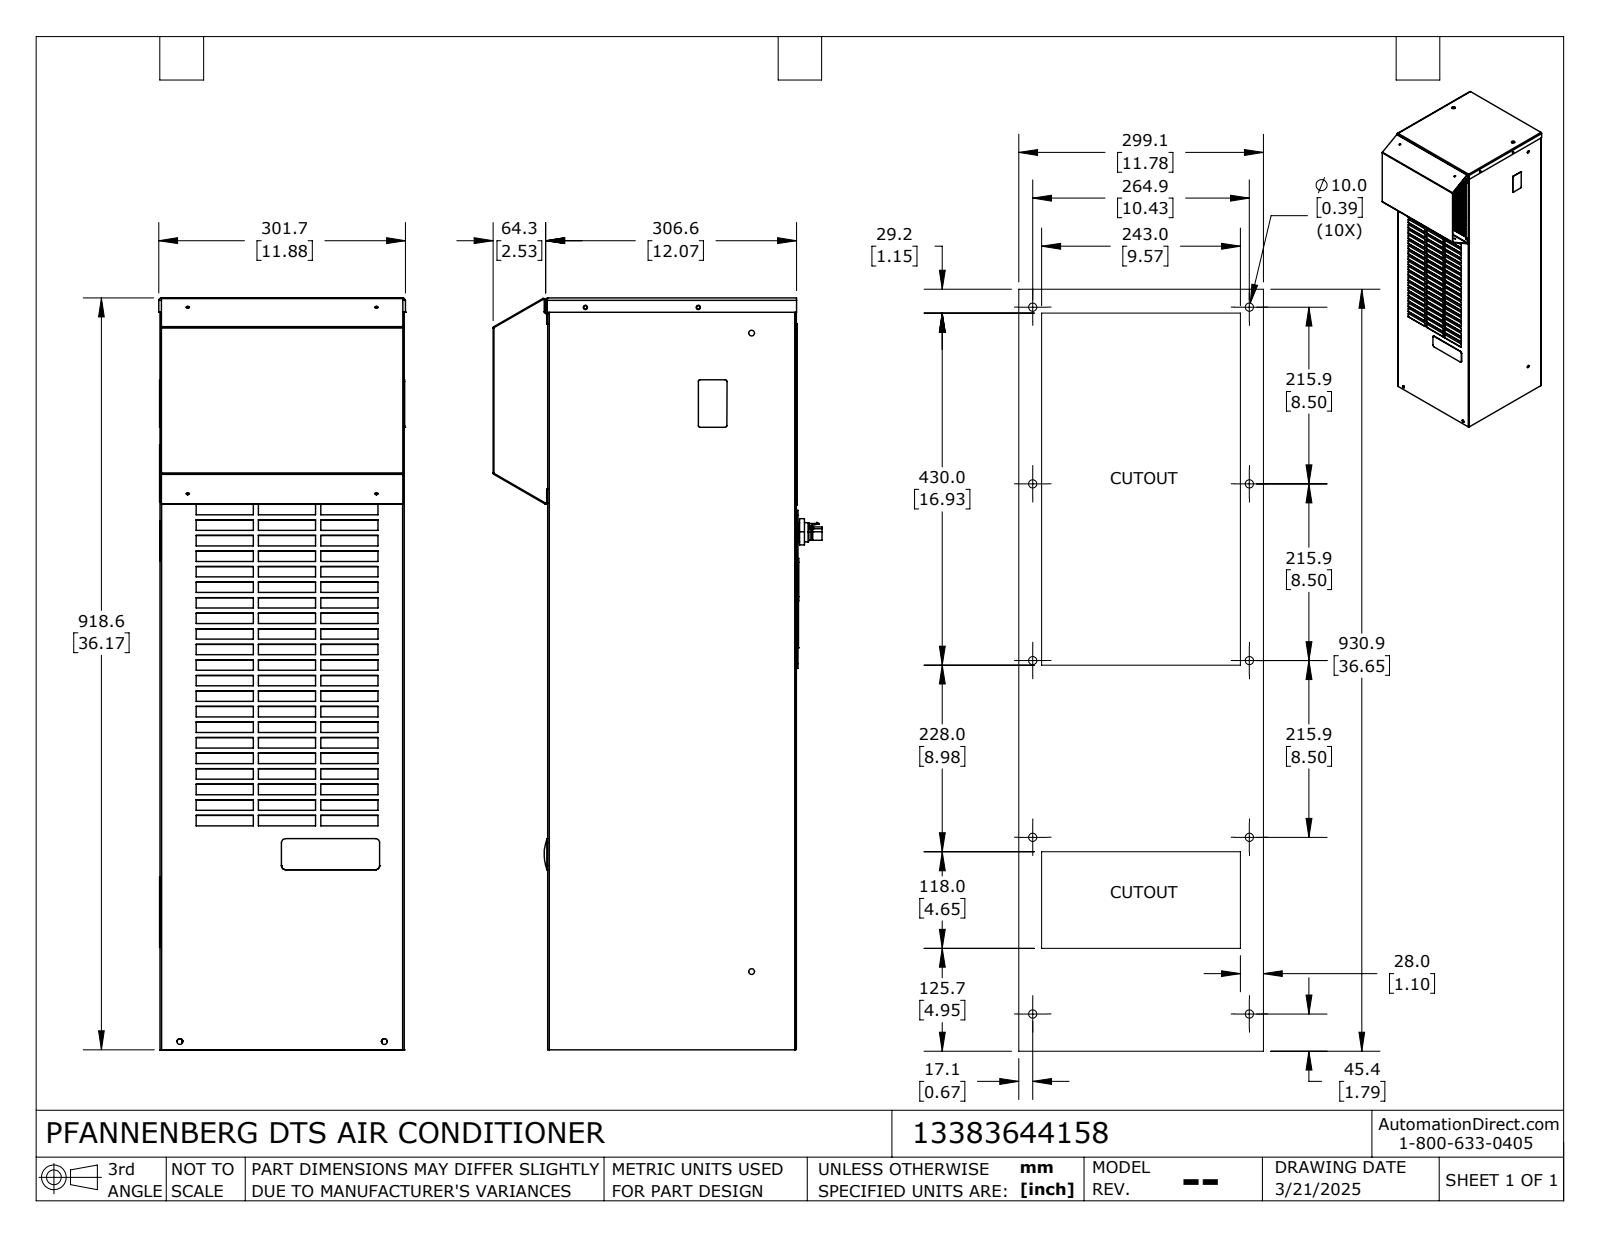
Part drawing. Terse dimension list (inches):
name: 13383644158_Default
written by: SolidWorks 2024 (CONFIG_CONTROL_DESIGN)
unit: in
bodies: 1 solid, 1788 faces (1242 planar, 493 cylindrical, 53 other)
size: 36.166 × 15.829 × 11.878
volume: 4 957 in³; area: 4 043 in²
holes: 35× ⌀0.165, 10× ⌀0.189, 6× ⌀0.276, 5× ⌀0.169, 5× ⌀0.209, 4× ⌀0.122, 4× ⌀0.161, 2× ⌀0.17, 2× ⌀0.203, 2× ⌀0.394, 2× ⌀0.945, 1× ⌀0.315
bosses: 4× ⌀0.079, 2× ⌀0.866, 1× ⌀1.378, 1× ⌀0.906
rounds: 112× R0.125, 19× R0.031, 12× R0.079, 12× R0.197, 10× R0.087, 10× R0.236, 8× R0.076, 4× R0.078
face distances: 11.812, 11.752, 0.045, 11.843, 0.031, 11.888, 0.076, 0.056, 0.027, 11.839
hole spacings: 0.244, 0.294, 0.294, 0.294, 0.454, 0.488, 1.496, 6.937
